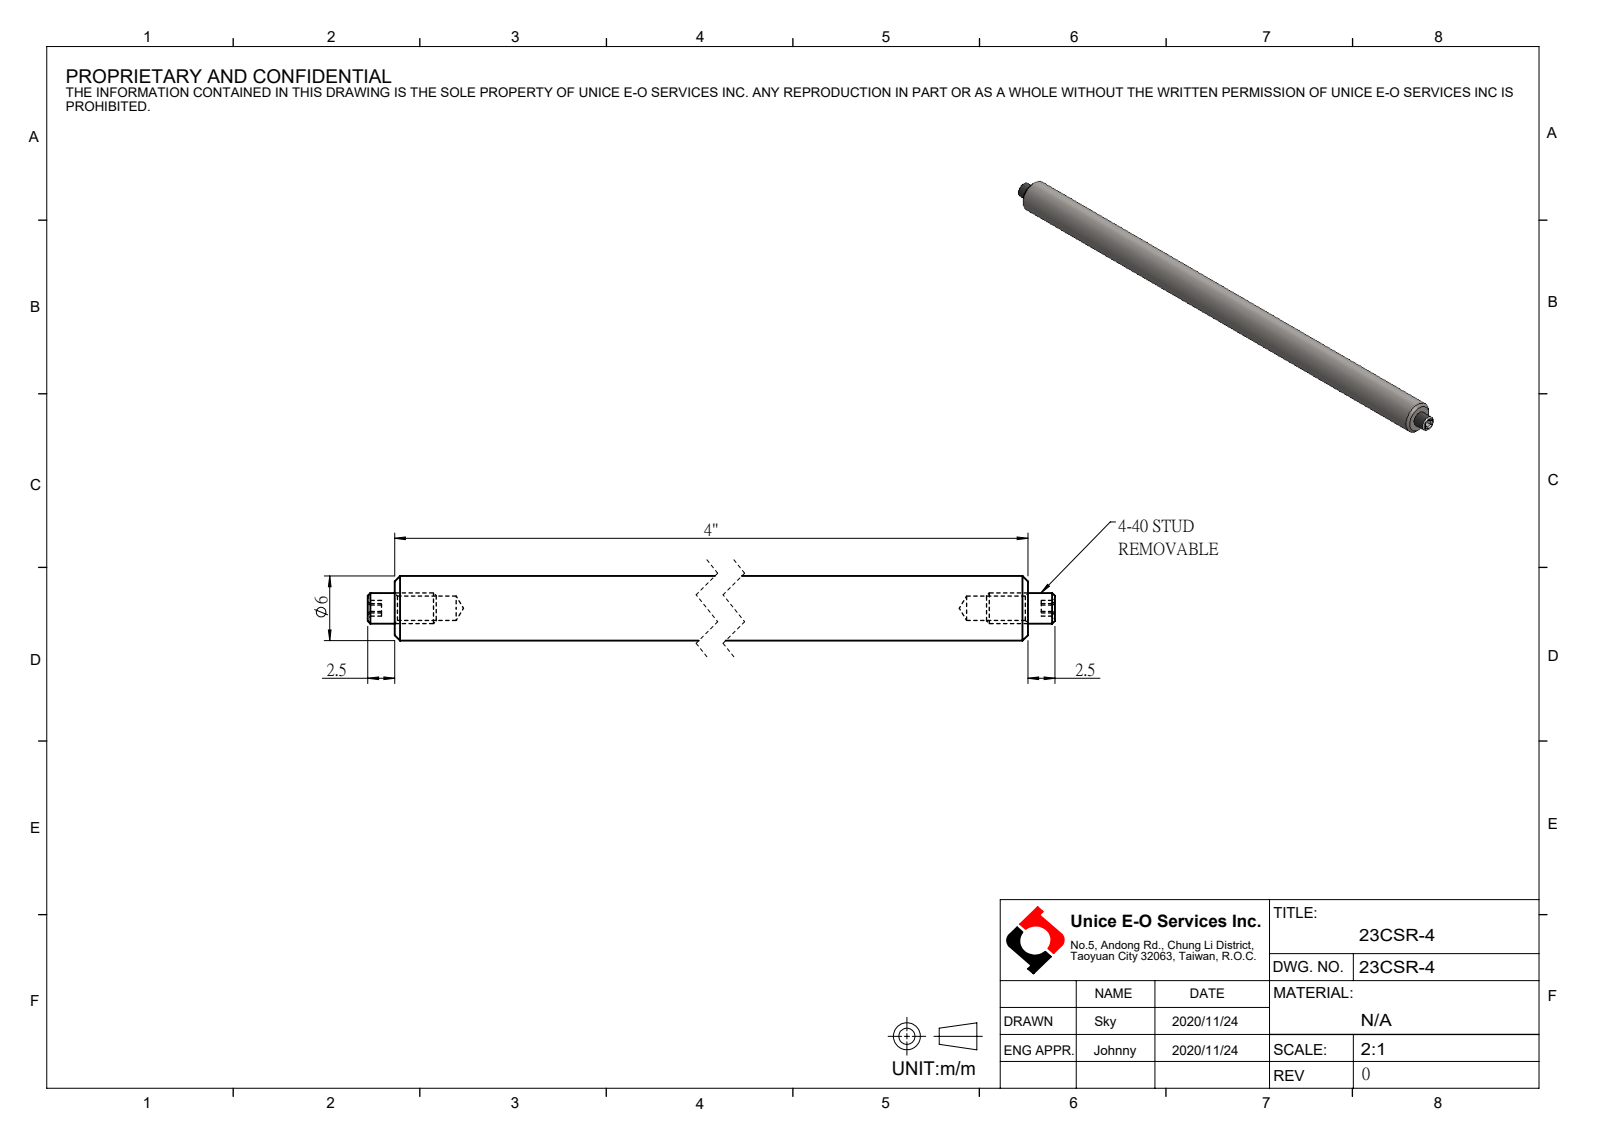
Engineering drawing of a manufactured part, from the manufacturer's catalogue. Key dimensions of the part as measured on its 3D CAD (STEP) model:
Part name (STEP PRODUCT): 23CSR-4
STEP written by: SolidWorks 2016 (AUTOMOTIVE_DESIGN)
Units: millimetres
Bodies: 0 solids, 42 faces (28 planar, 6 cylindrical, 8 other)
Overall size (bounding box): 106.6 × 6 × 6
Round bosses / shafts (diameter × count): ⌀6 ×1, ⌀2.84 ×1
Main face-to-face distances: 101.6, 1.27, 2.5, 104.1, 106.6
